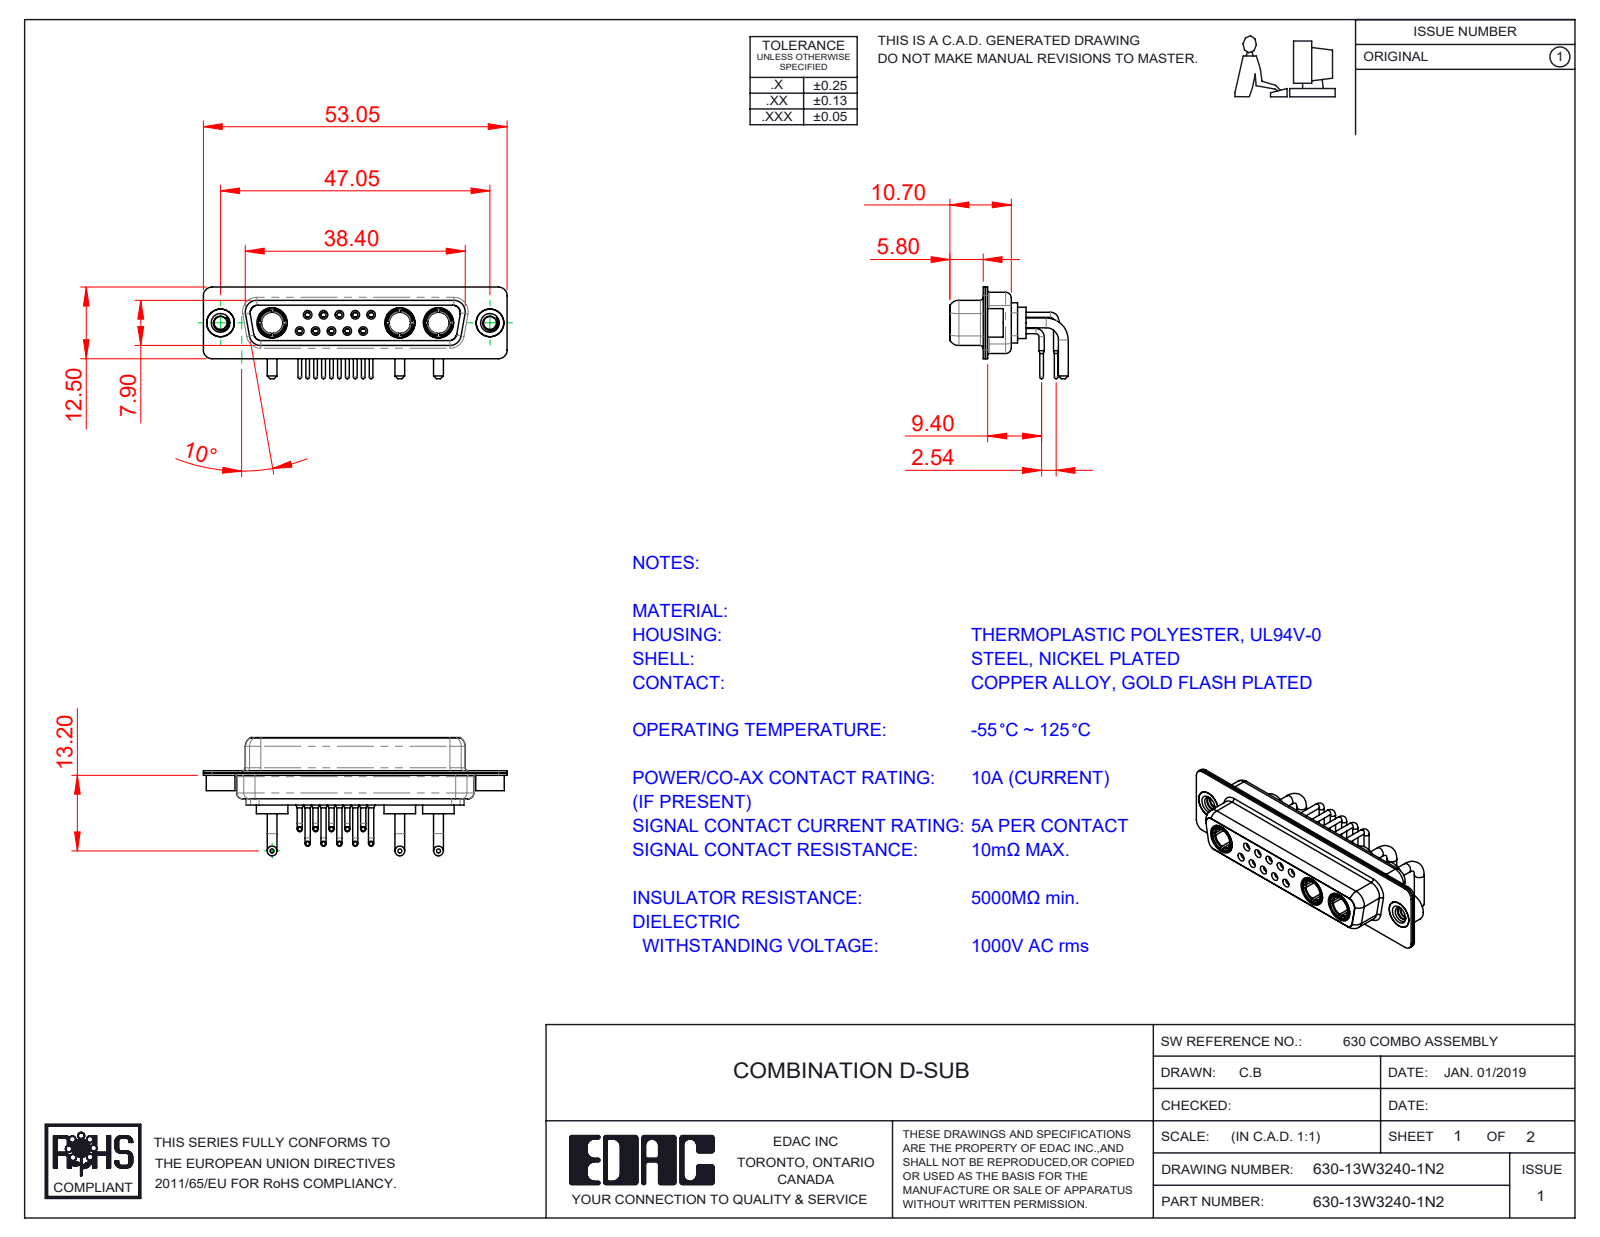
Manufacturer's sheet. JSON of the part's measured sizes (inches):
{"part_name": "630Combo Contact Row 2; 630Combo Contact Row 1; Power Socket_10A RA; 630Combo Shell Rear_25 Contacts (+4 more)", "step_written_by": "SolidWorks 2020 (CONFIG_CONTROL_DESIGN)", "units": "inches", "bodies": {"solids": 21, "faces": 1043, "planar": 304, "cylindrical": 442, "other": 297}, "overall_size": [2.089, 0.813, 0.63], "volume_in3": 0.235, "surface_area_in2": 13.74, "round_holes": [[0.035, 10], [0.043, 10], [0.059, 10], [0.079, 10], [0.063, 5], [0.067, 5], [0.191, 5], [0.146, 3], [0.209, 3], [0.089, 2], [0.157, 2], [0.159, 2]], "round_bosses_or_shafts": [[0.035, 10], [0.026, 10], [0.067, 6], [0.063, 5], [0.217, 3], [0.205, 3], [0.195, 3], [0.187, 3]], "partial_cylinders_radius": [[0.059, 16], [0.079, 12], [0.053, 8], [0.063, 8], [0.01, 4], [0.02, 4], [0.024, 4], [0.026, 4]], "face_to_face_distances": [0.016, 0.055, 0.018, 0.333, 0.35, 0.071, 0.244, 0.278, 0.295, 0.073], "hole_center_spacings": [0.124, 0.109, 0.218, 0.198, 0.198, 0.327, 0.294, 0.295]}
